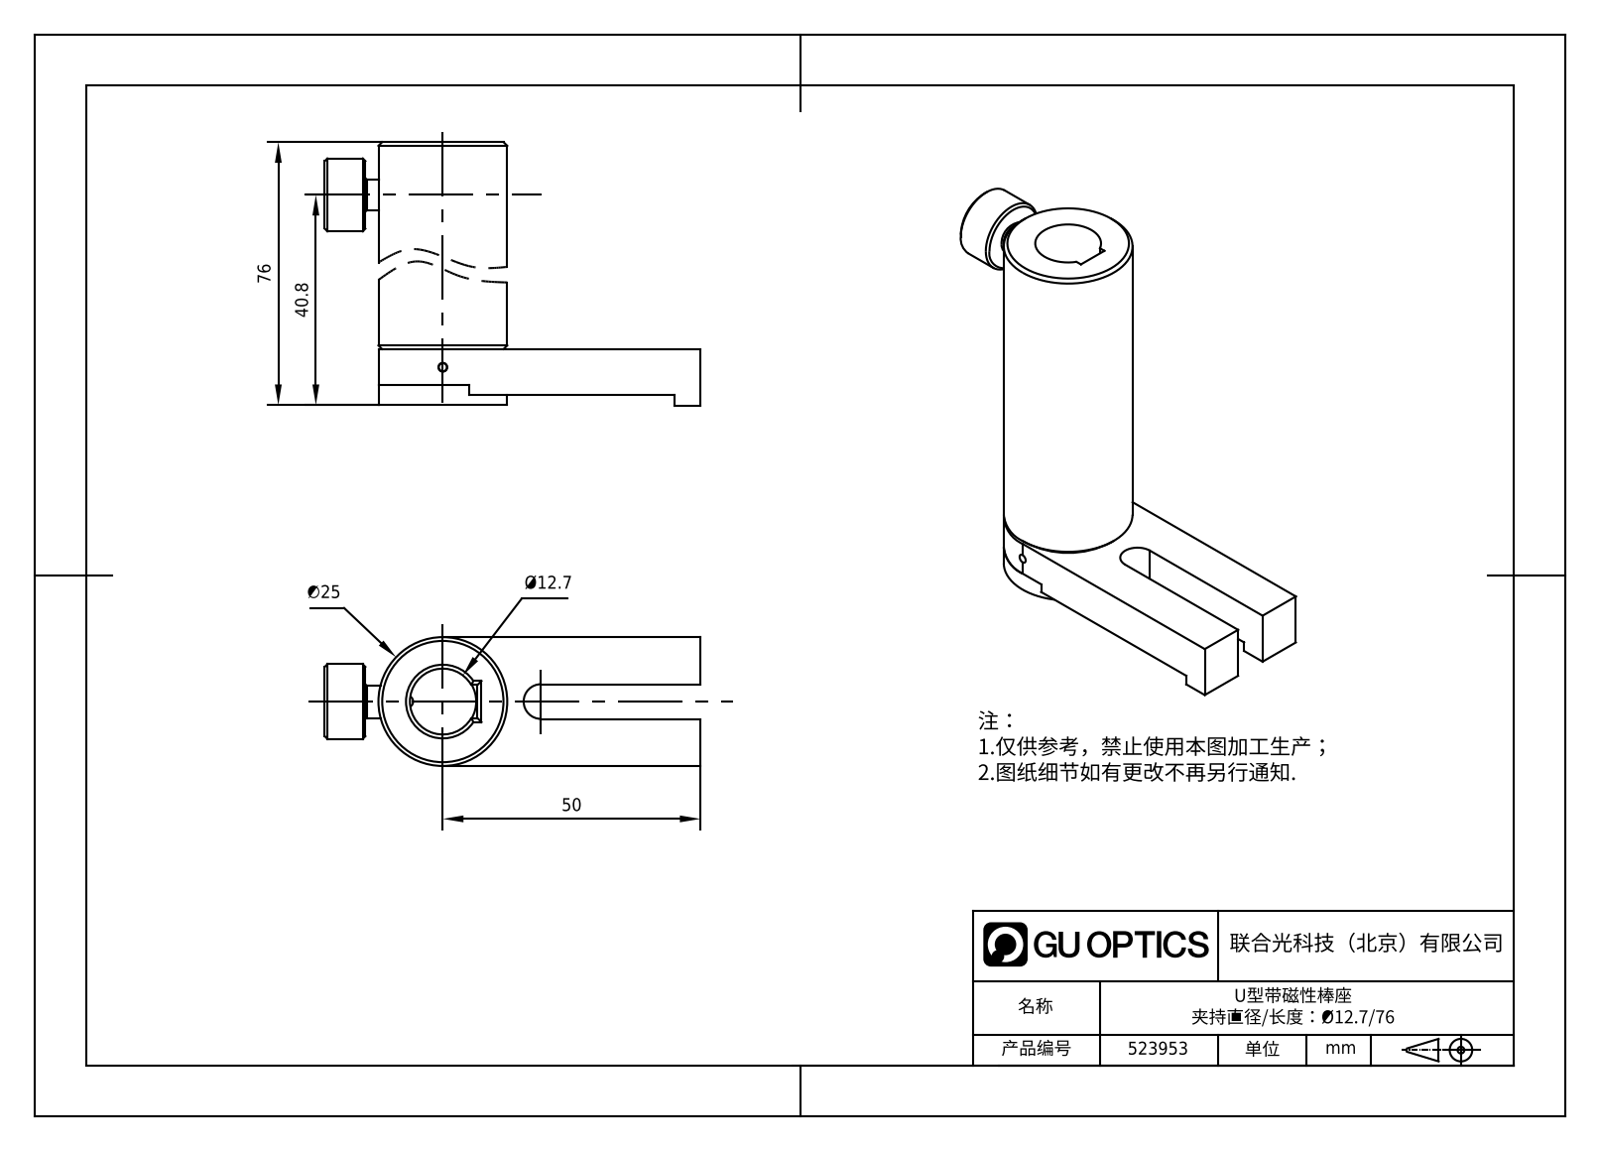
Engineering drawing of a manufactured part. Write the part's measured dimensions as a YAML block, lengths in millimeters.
part_name: "523953"
step_written_by: "SolidWorks 2016 (CONFIG_CONTROL_DESIGN)"
units: millimeters
bodies: {solids: 8, faces: 128, planar: 38, cylindrical: 50, other: 40}
overall_size: [77.03, 72.91, 24.99]
volume: 36244
surface_area: 16767
round_holes:
  - {diameter: 4.83, count: 3}
  - {diameter: 1.59, count: 1}
  - {diameter: 1.7, count: 1}
  - {diameter: 1.78, count: 1}
  - {diameter: 12.78, count: 1}
  - {diameter: 12.95, count: 1}
  - {diameter: 20.09, count: 1}
round_bosses_or_shafts:
  - {diameter: 4.76, count: 3}
  - {diameter: 24.99, count: 1}
  - {diameter: 20.05, count: 1}
  - {diameter: 17.78, count: 1}
  - {diameter: 17.27, count: 1}
  - {diameter: 14.12, count: 1}
  - {diameter: 5.99, count: 1}
  - {diameter: 3, count: 1}
partial_cylinders:
  - {radius: 3.37, count: 1}
  - {radius: 12.95, count: 1}
face_to_face_distances: [8.89, 9.13, 15.87, 25, 1.83, 7.06, 1.98, 3.81, 10.87, 76]
hole_center_spacings: [16.5, 9.53, 9.52]
